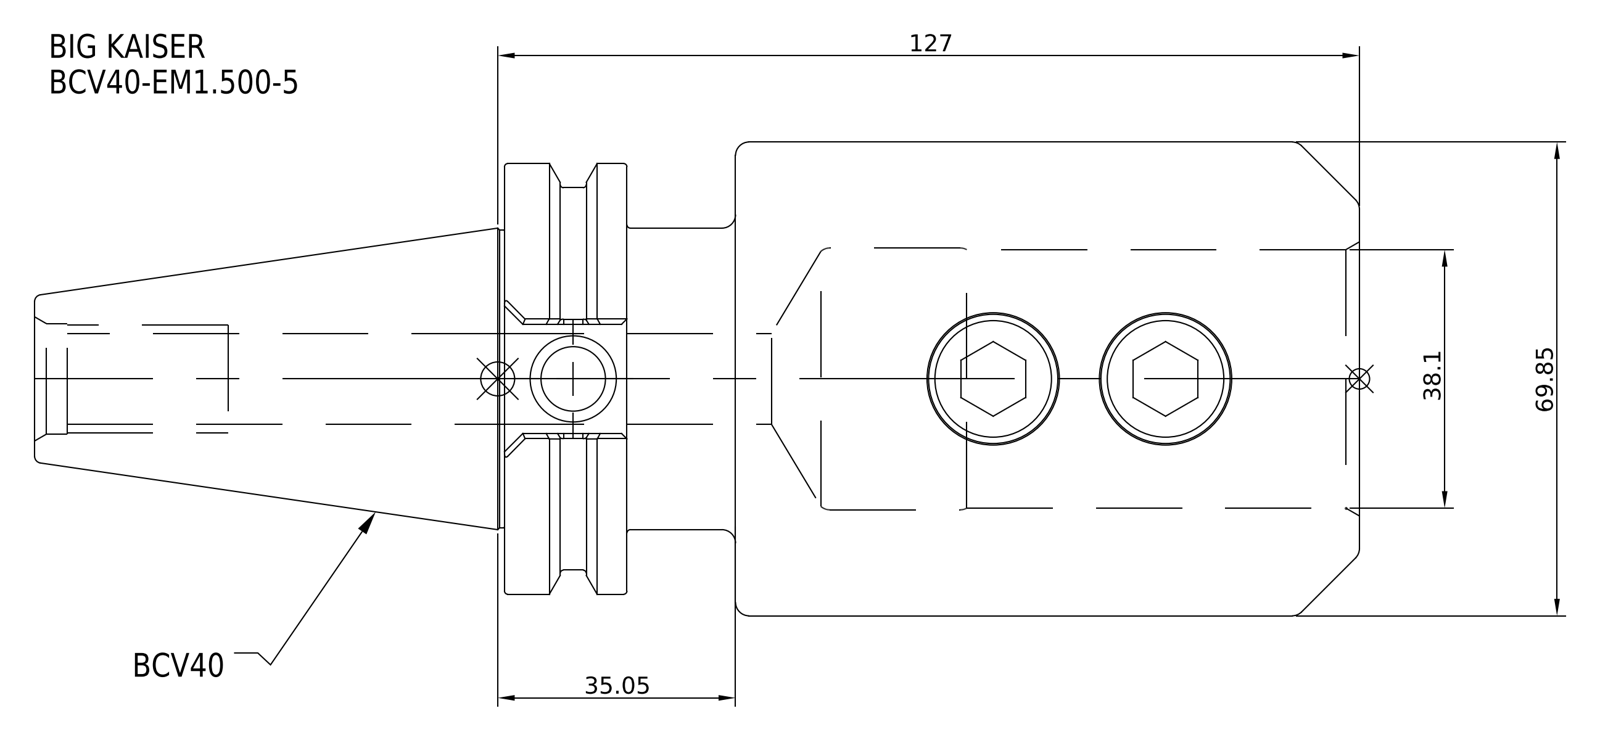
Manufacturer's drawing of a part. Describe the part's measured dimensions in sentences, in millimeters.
The part is named "BCV40-EM1_500-5". Its 3-D file was written by "SolidWorks 2021 (CONFIG_CONTROL_DESIGN)". It is 1 solid with 30 faces: 8 planar, 14 cylindrical and 8 other. Overall it measures 195.25 by 69.85 by 69.85 millimeters. Its volume is 384 879 cubic millimeters and its surface area 53 954 square millimeters. Round holes: 1 of diameter 38.1. Round bosses or shafts: 1 of diameter 69.85, 1 of diameter 63.5, 1 of diameter 56.36, 1 of diameter 44.45. The main face-to-face distances are 34.05, 16, 18.05, 91.95, 107.95, 126, 195.25, 103.3, 87.3, 69.25.
